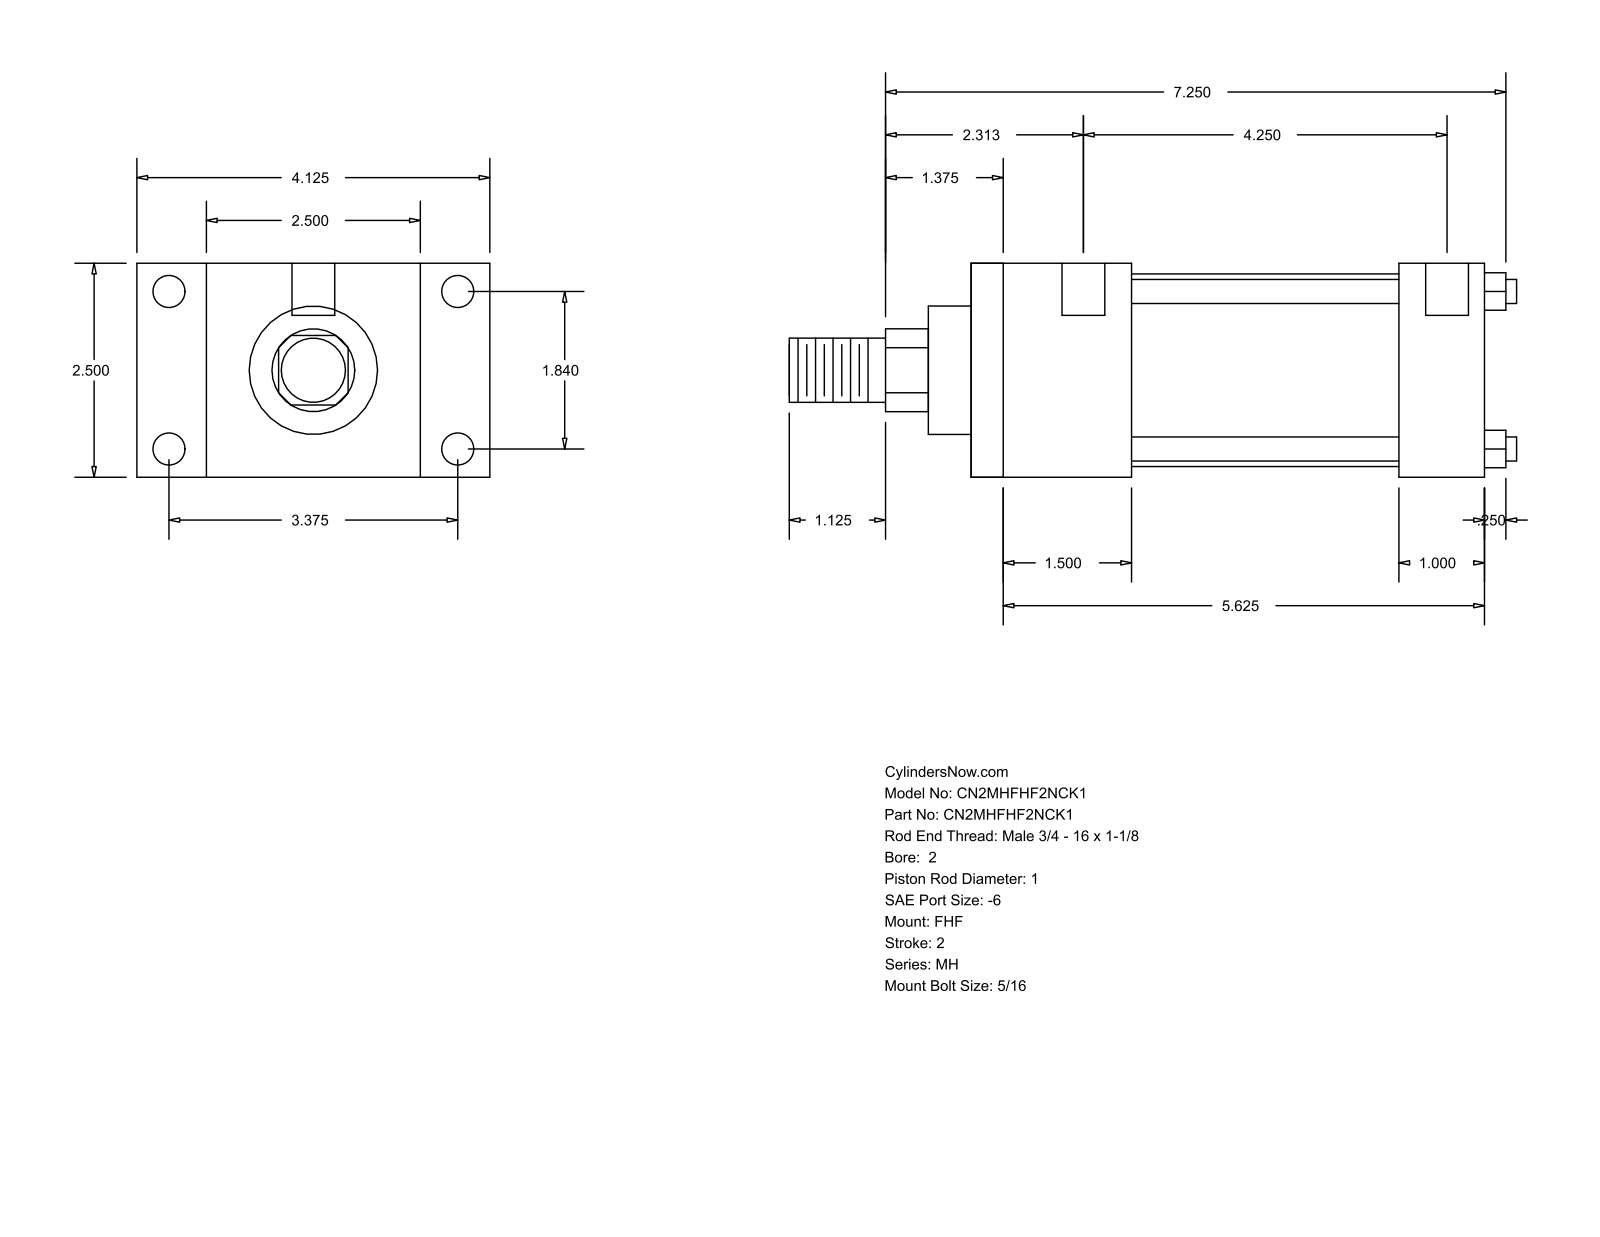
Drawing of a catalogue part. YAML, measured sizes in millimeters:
part_name: "MH_FHF__0200_1"
step_written_by: "GSSL Pune (CONFIG_CONTROL_DESIGN)"
units: millimeters
bodies: {solids: 0, faces: 88, planar: 60, cylindrical: 28, other: 0}
overall_size: [215.9, 104.78, 63.5]
round_holes:
  - {diameter: 5.56, count: 4}
  - {diameter: 9.53, count: 4}
  - {diameter: 12.7, count: 2}
round_bosses_or_shafts:
  - {diameter: 7.14, count: 4}
  - {diameter: 57.15, count: 1}
  - {diameter: 38.1, count: 1}
  - {diameter: 25.4, count: 1}
  - {diameter: 19.05, count: 1}
partial_cylinders:
  - {radius: 12.29, count: 1}
face_to_face_distances: [63.5, 152.4, 104.77, 47.63, 20.64, 84.14, 104.78, 25.4, 127, 79.37]
hole_center_spacings: [46.74, 85.72, 97.63, 115.88, 3.17, 4.76, 107.95, 111.12]
